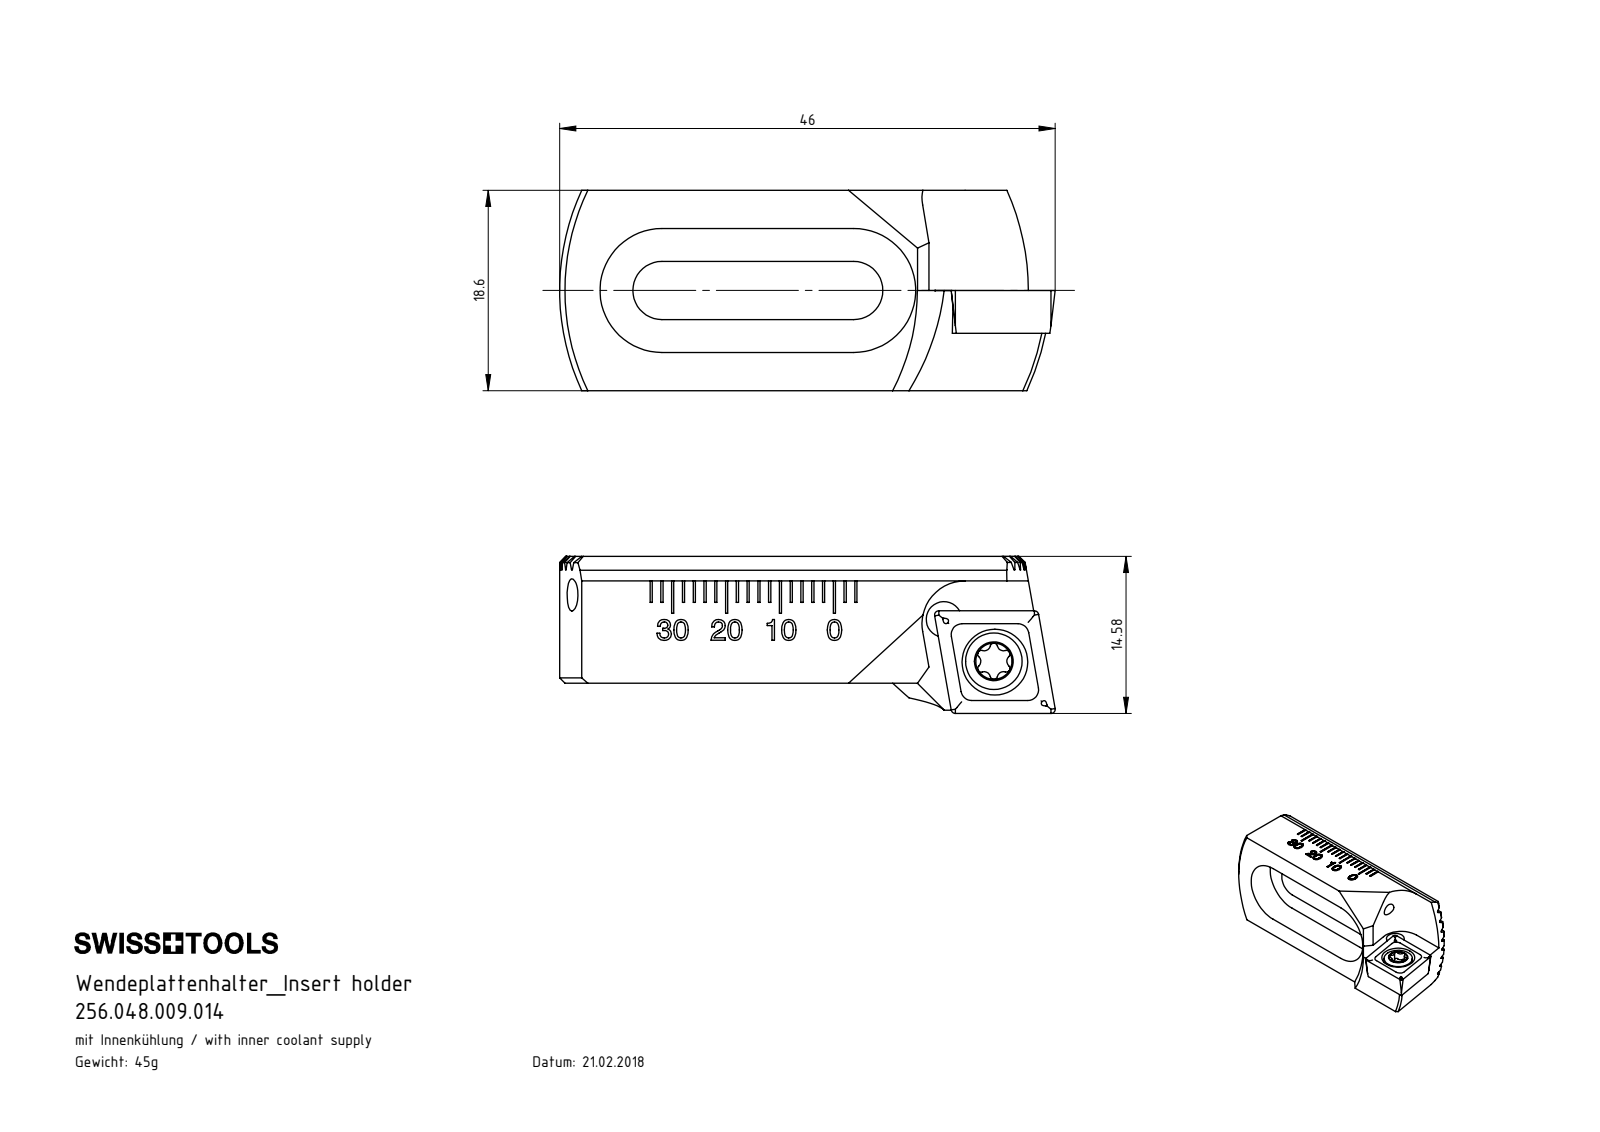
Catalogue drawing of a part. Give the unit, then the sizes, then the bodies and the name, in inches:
Units: inches
Overall size (bounding box): 1.811 × 0.732 × 0.574
Round holes (diameter × count): ⌀0.079 ×3, ⌀0.13 ×2, ⌀0.094 ×1, ⌀0.173 ×1, ⌀0.24 ×1
Round bosses / shafts (diameter × count): ⌀0.207 ×1, ⌀0.157 ×1, ⌀0.118 ×1
Partial cylindrical surfaces — rounded edges, fillets, slot ends (radius × count): R0.006 ×10, R0.013 ×6, R0.023 ×6, R0.106 ×2, R0.226 ×2, R0.157 ×1, R0.866 ×1, R0.906 ×1
Main face-to-face distances: 0.068, 0.136, 0.341, 0.409, 0.273, 0.732, 0.477, 0.472, 0.26, 0.205
Hole centre spacings: 0.25, 0.255
Volume: 0.351 in³ · Surface area: 7.153 in²
Bodies: 5 solids, 444 faces (210 planar, 77 cylindrical, 157 other)
Part name (STEP PRODUCT): 256.048.009.014; KVT_MB_600_030; WCB-ER2.001.009_A; CCMT09T304 (+1 more)
STEP written by: SolidWorks 2017 (CONFIG_CONTROL_DESIGN)
